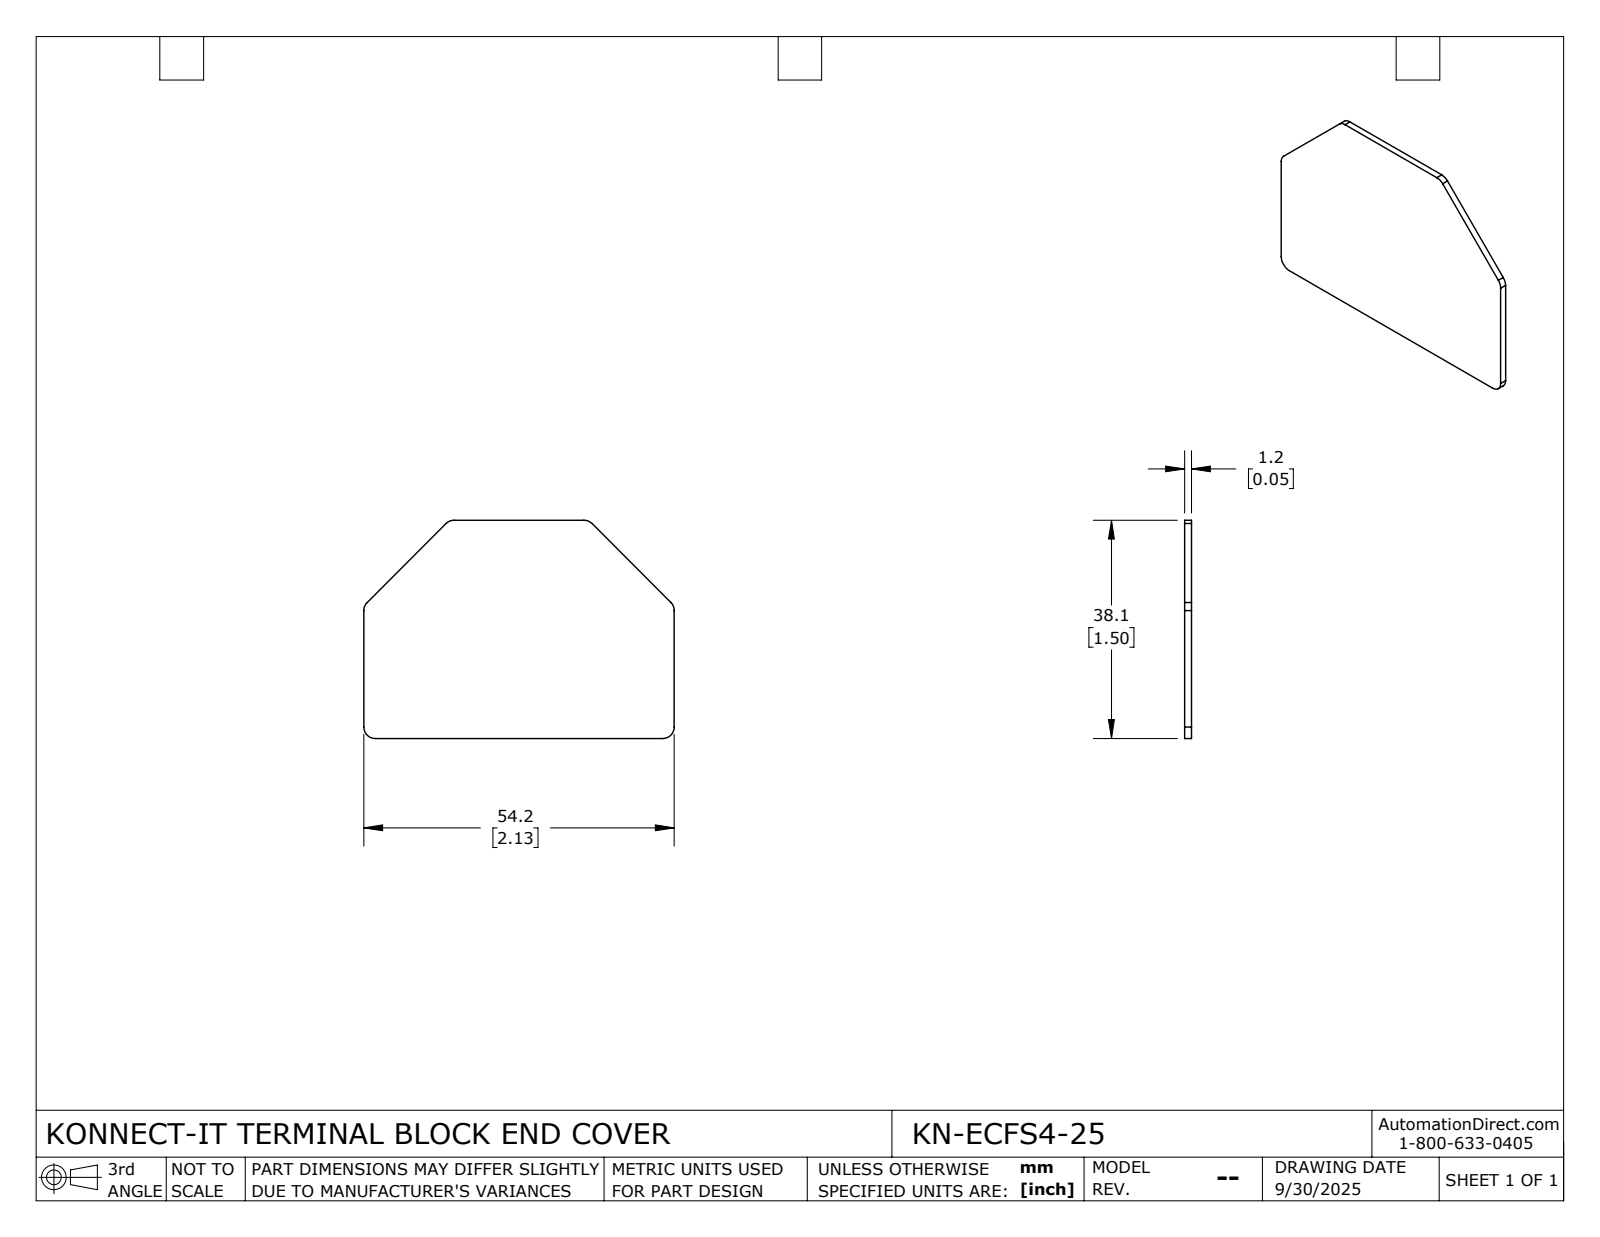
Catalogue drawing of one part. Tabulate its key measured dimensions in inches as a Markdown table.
| quantity | value |
| --- | --- |
| part name | KN-ECFS4-25 |
| STEP written by | SolidWorks 2024 (CONFIG_CONTROL_DESIGN) |
| units | inches |
| bodies | 1 solid, 14 faces (8 planar, 6 cylindrical, 0 other) |
| overall size | 2.134 × 1.5 × 0.047 |
| volume | 0.135 in³ |
| surface area | 6.011 in² |
| partial cylindrical surfaces (radius × count) | 0.079 × 6 |
| main face-to-face distances | 0.047, 1.5, 2.134 |
